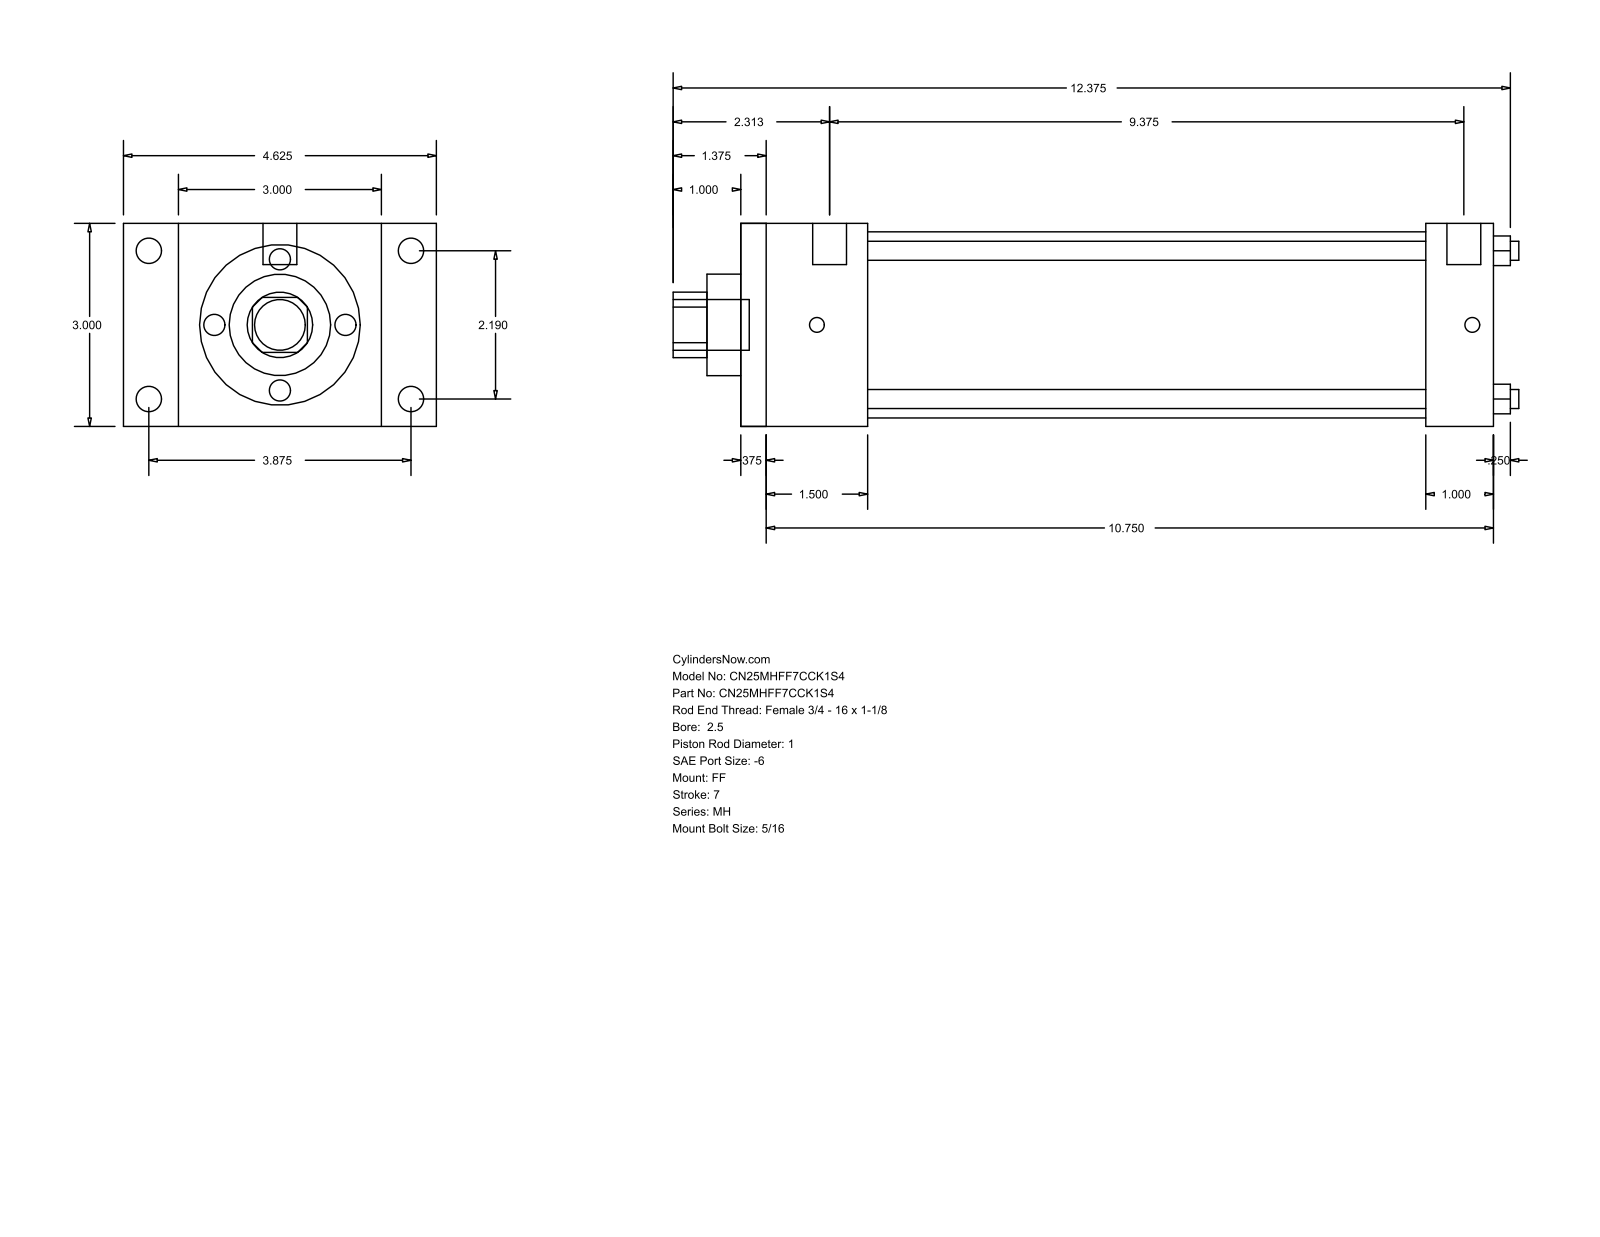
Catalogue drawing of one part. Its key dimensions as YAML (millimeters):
part_name: "MH_FF__0250_1"
step_written_by: "GSSL Pune (CONFIG_CONTROL_DESIGN)"
units: millimeters
bodies: {solids: 0, faces: 92, planar: 64, cylindrical: 28, other: 0}
overall_size: [317.5, 117.47, 76.2]
round_holes:
  - {diameter: 7.14, count: 4}
  - {diameter: 25.4, count: 1}
  - {diameter: 38.1, count: 1}
  - {diameter: 69.85, count: 1}
round_bosses_or_shafts:
  - {diameter: 9.53, count: 4}
  - {diameter: 5.56, count: 4}
  - {diameter: 12.7, count: 2}
  - {diameter: 19.05, count: 1}
partial_cylinders:
  - {radius: 12.29, count: 1}
face_to_face_distances: [76.2, 282.58, 9.52, 273.06, 47.63, 257.17, 38.11, 247.65, 209.54, 234.95]
hole_center_spacings: [39.33, 55.62, 78.66]
